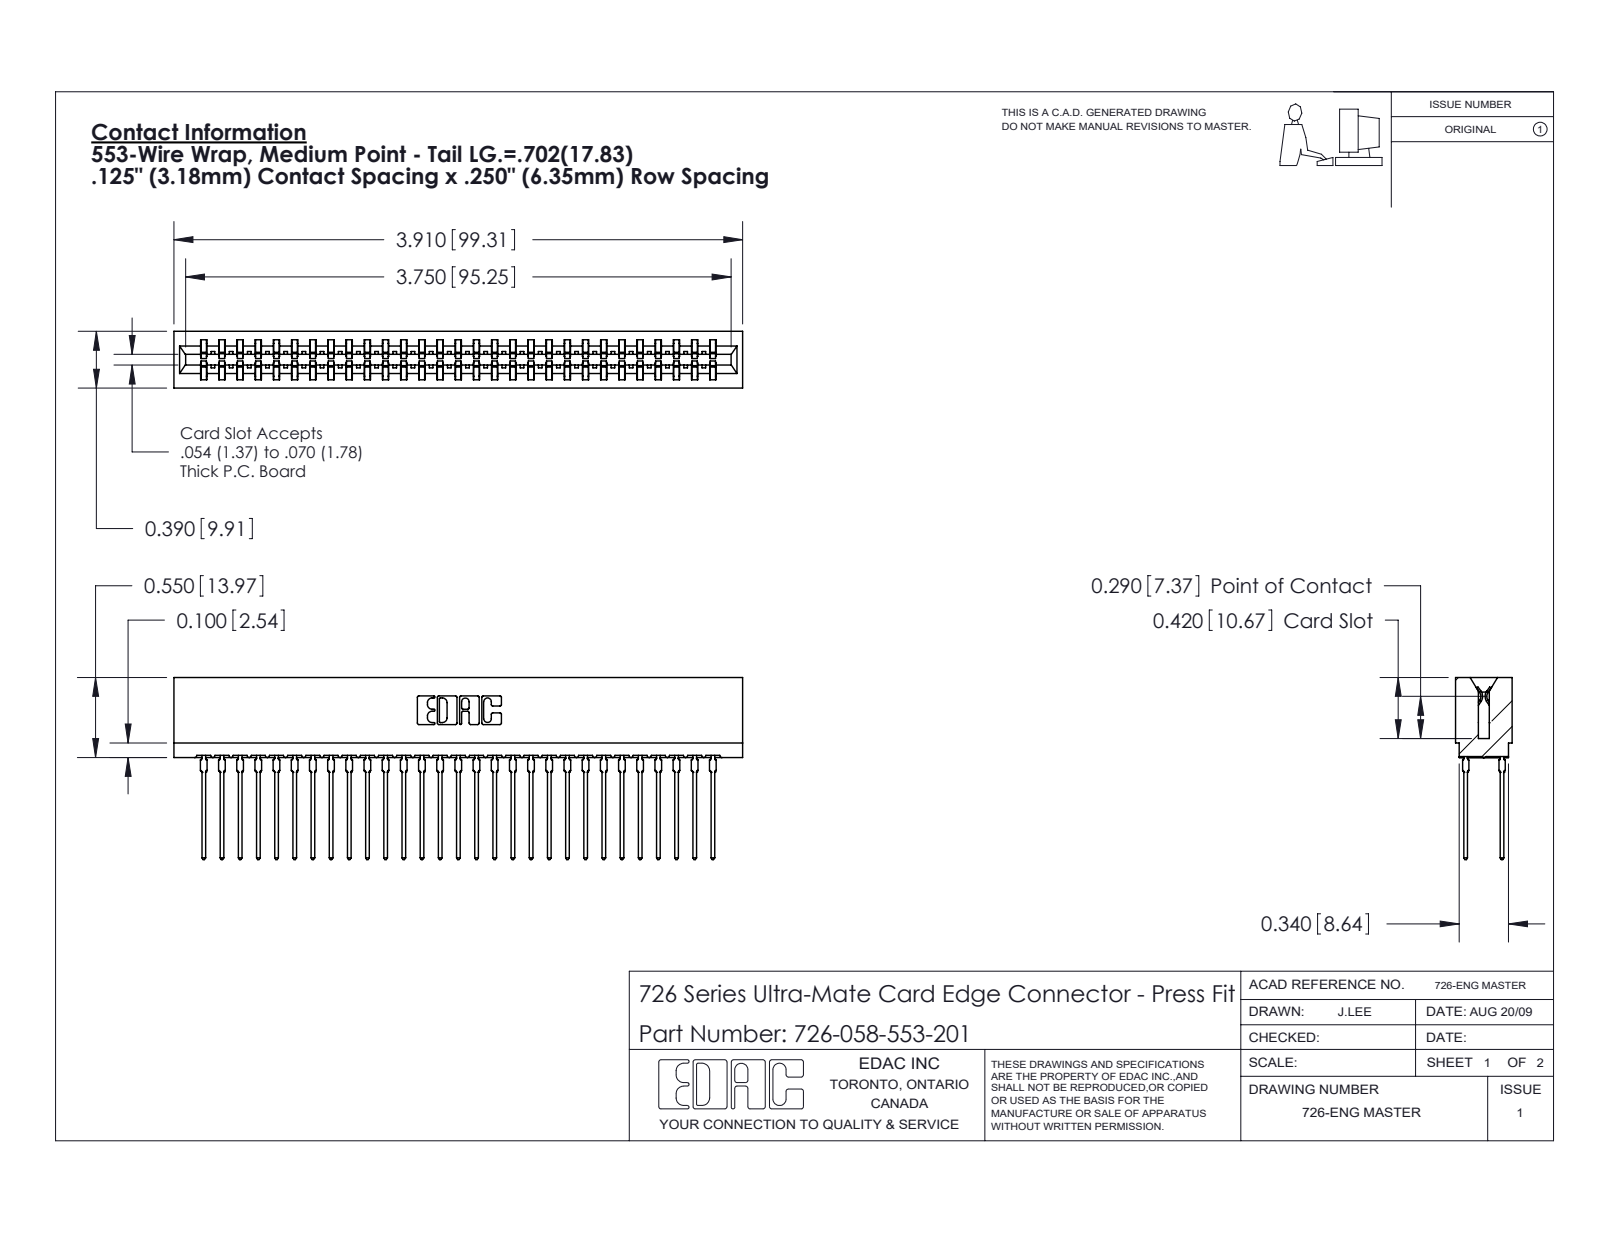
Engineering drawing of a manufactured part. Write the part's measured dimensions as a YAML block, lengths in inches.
part_name: "726 Part_.515 Slot Depth - 01; 726-058-553-201; 746-292-001_553"
step_written_by: "SolidWorks 2020 (CONFIG_CONTROL_DESIGN)"
units: inches
bodies: {solids: 59, faces: 5288, planar: 2723, cylindrical: 1057, other: 1508}
overall_size: [3.91, 1.251, 0.39]
volume: 0.578
surface_area: 25.92
partial_cylinders:
  - {radius: 0.021, count: 116}
  - {radius: 0.015, count: 30}
  - {radius: 0.01, count: 22}
  - {radius: 0.005, count: 8}
  - {radius: 0.011, count: 8}
  - {radius: 0.007, count: 6}
  - {radius: 0.031, count: 6}
  - {radius: 0.026, count: 3}
face_to_face_distances: [0.057, 0.333, 0.025, 0.307, 0.25, 0.083, 0.39, 0.275, 0.5, 0.225]
